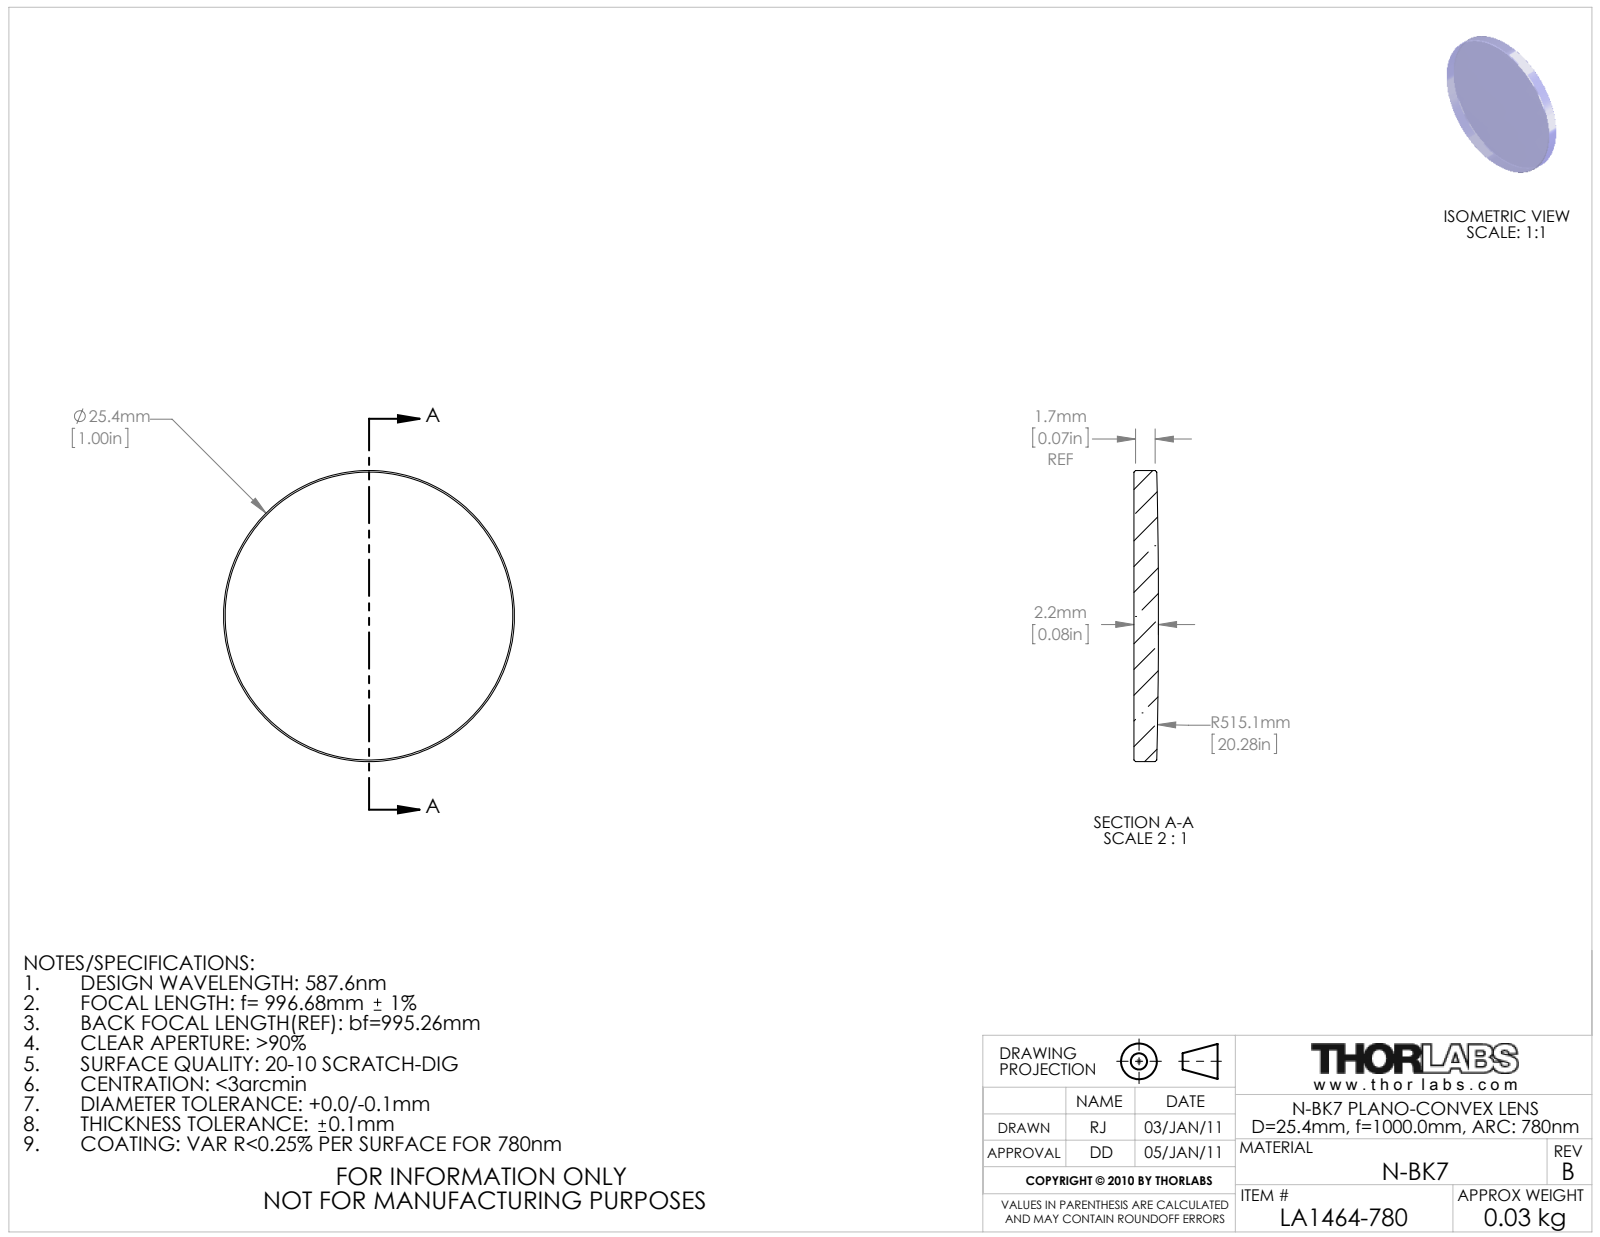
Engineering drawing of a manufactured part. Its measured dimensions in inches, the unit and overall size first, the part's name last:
Units: inches
Overall size (bounding box): 1 × 1 × 0.085
Round bosses / shafts (diameter × count): ⌀1 ×1
Bodies: 0 solids, 9 faces (1 planar, 2 cylindrical, 6 other)
Part name (STEP PRODUCT): 21808-E0W
STEP written by: SolidWorks 2011 (AUTOMOTIVE_DESIGN)
